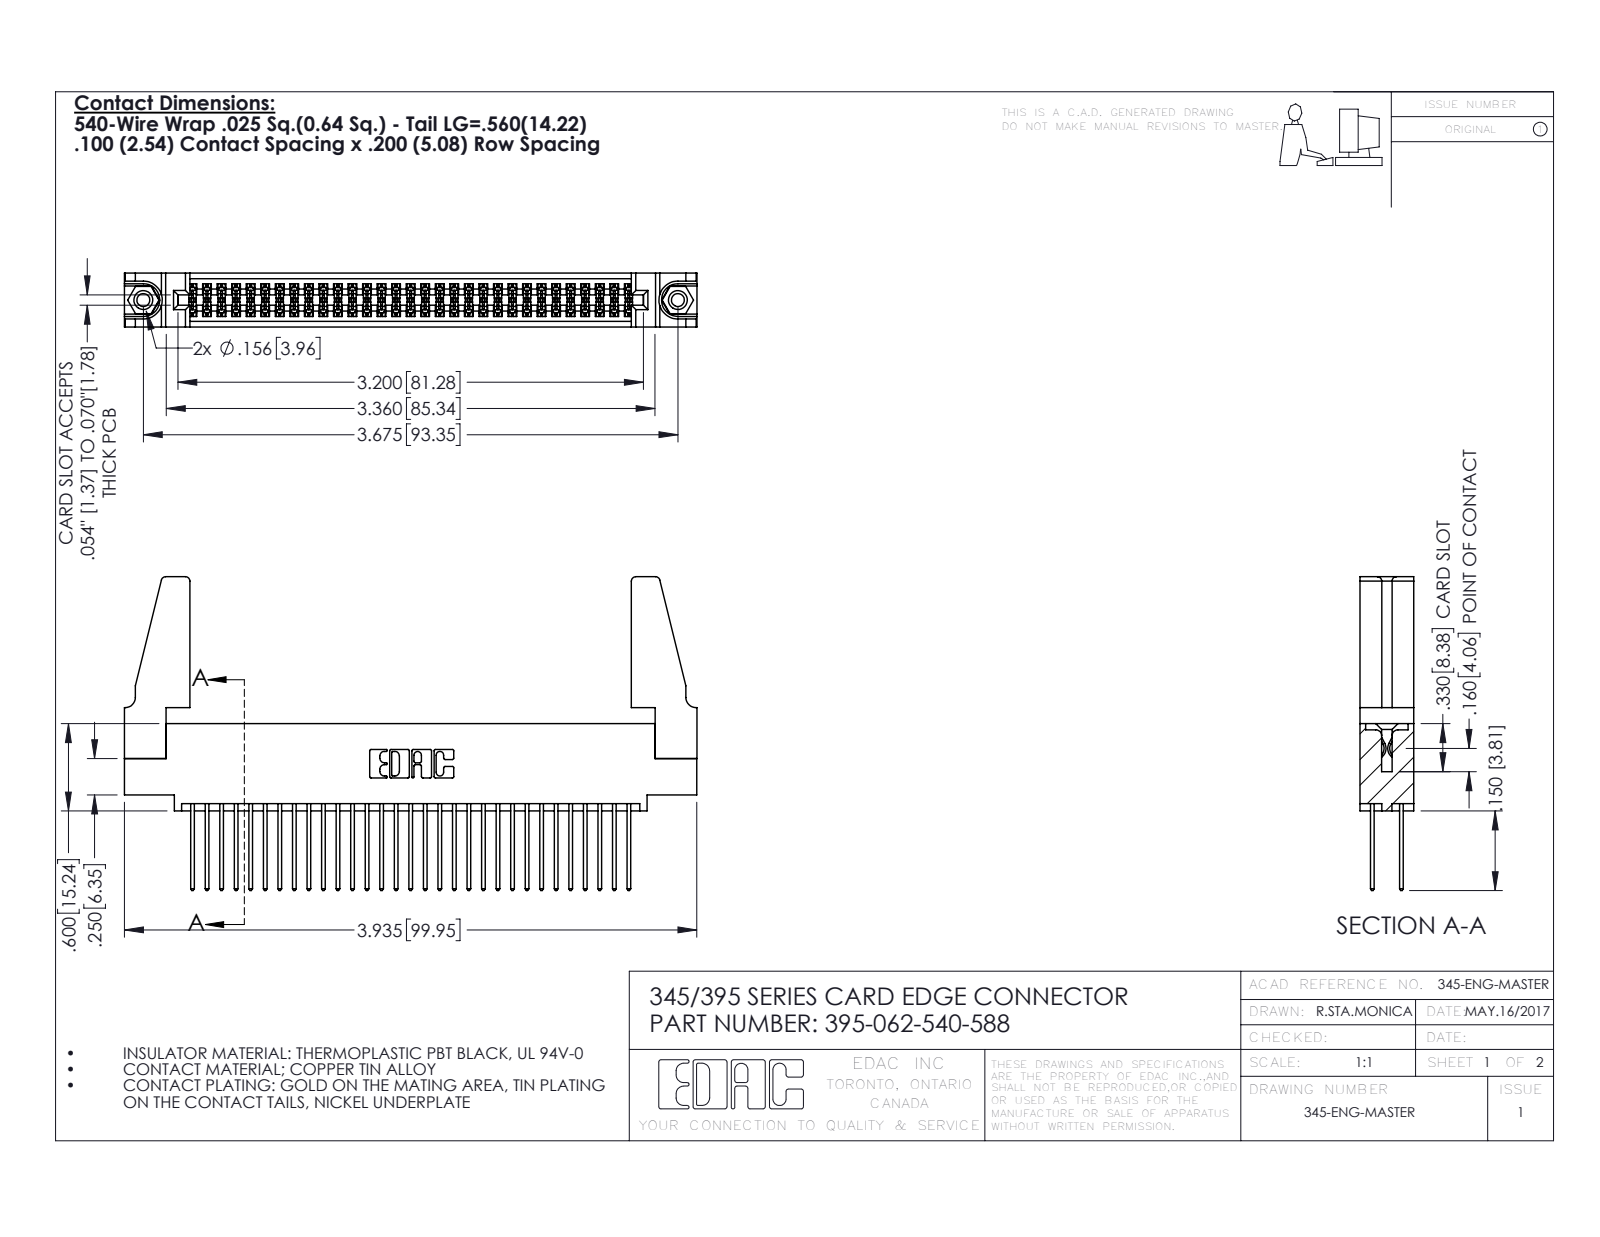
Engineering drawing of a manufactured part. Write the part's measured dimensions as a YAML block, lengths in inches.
part_name: "345 Part_0.110 Offset - 0.156 Dia-TH; 345-220-078_345-220-088; 395-062-540-588; 345-292-001_345-293-140 (+1 more)"
step_written_by: "SolidWorks 2016 (CONFIG_CONTROL_DESIGN)"
units: inches
bodies: {solids: 67, faces: 3354, planar: 2202, cylindrical: 1136, other: 16}
overall_size: [3.936, 2.157, 0.37]
volume: 0.795
surface_area: 28.73
round_holes:
  - {diameter: 0.089, count: 2}
  - {diameter: 0.125, count: 2}
  - {diameter: 0.156, count: 2}
  - {diameter: 0.064, count: 1}
round_bosses_or_shafts:
  - {diameter: 0.155, count: 2}
partial_cylinders:
  - {radius: 0.006, count: 93}
  - {radius: 0.01, count: 62}
  - {radius: 0.01, count: 22}
  - {radius: 0.03, count: 8}
  - {radius: 0.007, count: 6}
  - {radius: 0.031, count: 6}
  - {radius: 0.026, count: 3}
  - {radius: 0.014, count: 2}
face_to_face_distances: [0.072, 0.298, 0.37, 0.2, 0.098, 0.272, 0.025, 0.225, 0.175, 0.149]
hole_center_spacings: [0.27, 3.44, 3.675]
